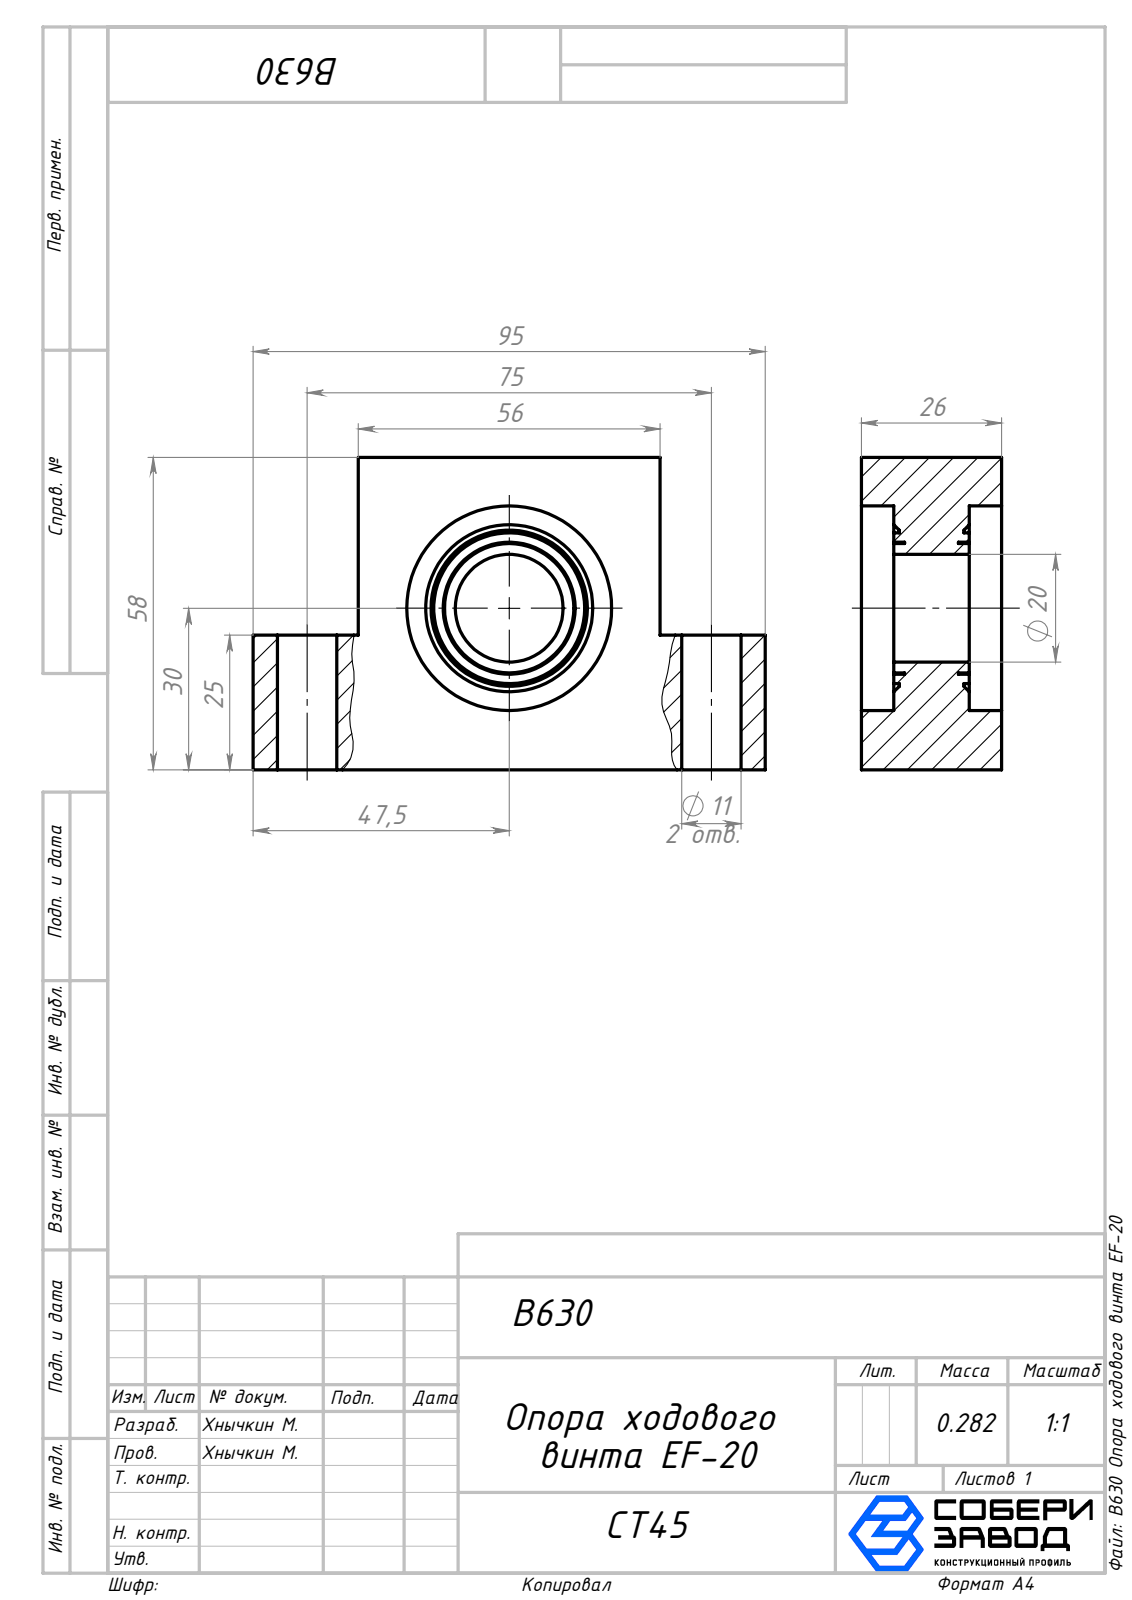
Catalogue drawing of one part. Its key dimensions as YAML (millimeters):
part_name: "B630 Опора ходового винта EF-20"
step_written_by: "SolidWorks 2026 (AUTOMOTIVE_DESIGN)"
units: millimeters
bodies: {solids: 1, faces: 46, planar: 20, cylindrical: 22, other: 4}
overall_size: [95, 58, 26]
volume: 86780
surface_area: 20297
round_holes:
  - {diameter: 11, count: 2}
  - {diameter: 20, count: 1}
  - {diameter: 24.5, count: 1}
  - {diameter: 38, count: 1}
round_bosses_or_shafts:
  - {diameter: 28, count: 1}
  - {diameter: 24, count: 1}
face_to_face_distances: [26, 58, 6, 20, 19.5, 75.5, 56, 25, 33, 14]
hole_center_spacings: [75]
